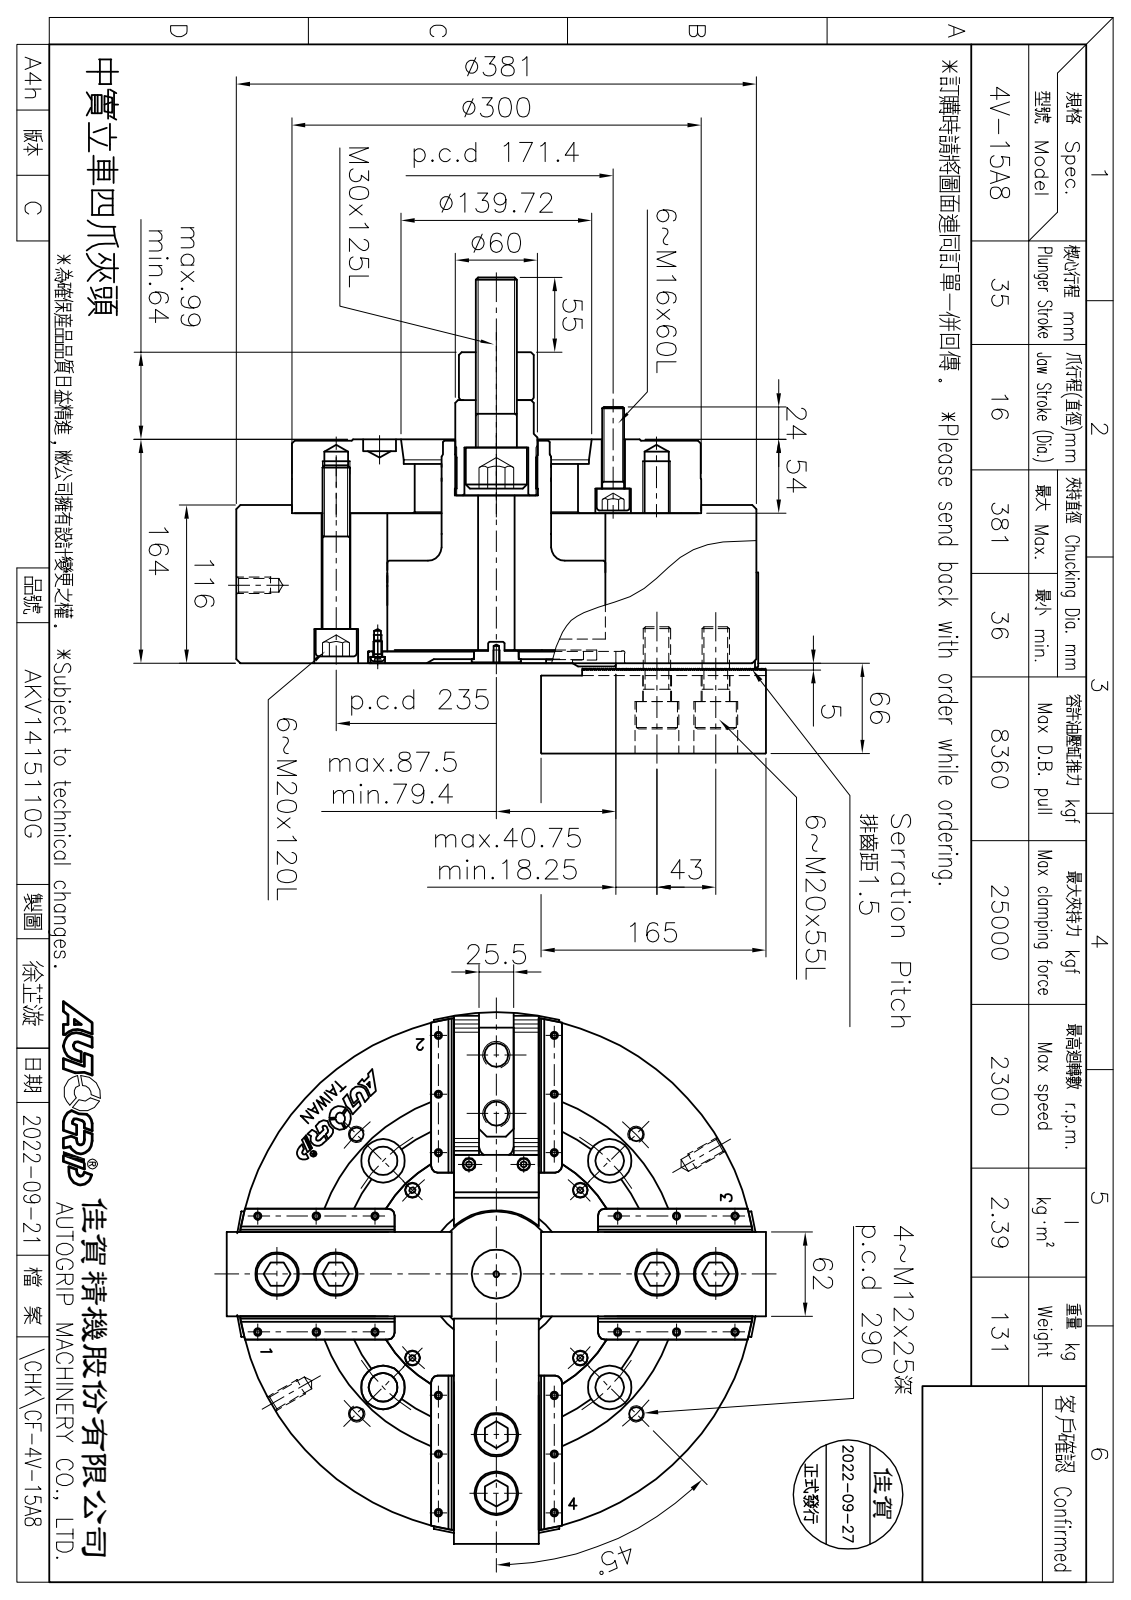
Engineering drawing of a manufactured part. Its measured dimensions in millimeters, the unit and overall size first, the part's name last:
Units: millimetres
Overall size (bounding box): 416.5 × 416.5 × 349.2
Round holes (diameter × count): ⌀5.5 ×32, ⌀5 ×25, ⌀4.2 ×24, ⌀17.5 ×12, ⌀21 ×12, ⌀32 ×12, ⌀9.5 ×8, ⌀20 ×8, ⌀17 ×6, ⌀26 ×6, ⌀6 ×4, ⌀6.6 ×4
Round bosses / shafts (diameter × count): ⌀9.5 ×24, ⌀30 ×12, ⌀5 ×11, ⌀8.5 ×8, ⌀24 ×6, ⌀16 ×6, ⌀20 ×4, ⌀10.5 ×4
Partial cylindrical surfaces — rounded edges, fillets, slot ends (radius × count): R0.1 ×720, R2 ×8, R5 ×8, R13.25 ×4, R13.5 ×4, R190.5 ×4, R76 ×1
Main face-to-face distances: 110, 62, 8.5, 6, 1, 154.5, 163, 53, 58, 116
Hole centre spacings: 43, 95.26, 85, 146.21, 169.1, 186.64, 33.42, 41.02
Volume: 17 980 000 mm³ · Surface area: 1 687 000 mm²
Bodies: 96 solids, 8812 faces (6197 planar, 2094 cylindrical, 521 other)
Part name (STEP PRODUCT): SJ-15P; CF-4V-15-04000; 3P-15連接管螺栓; CF-4V-15-03000 (+8 more)
STEP written by: SolidWorks 2016 (CONFIG_CONTROL_DESIGN)
